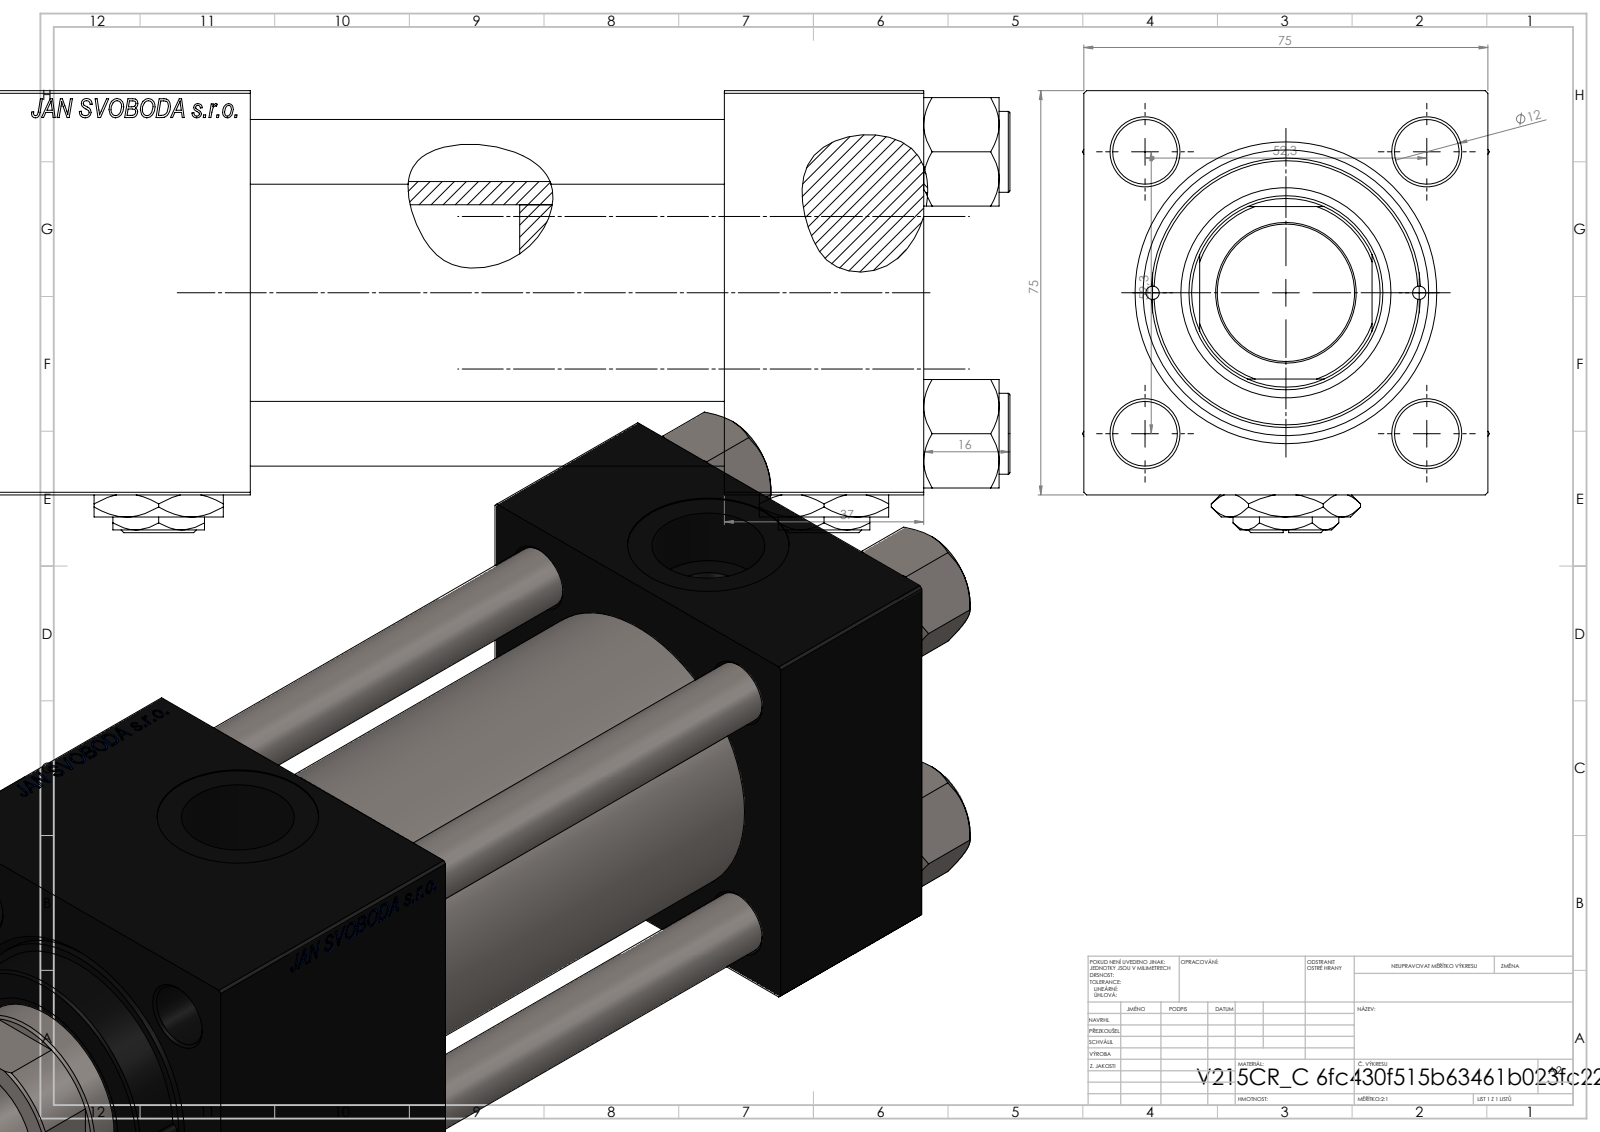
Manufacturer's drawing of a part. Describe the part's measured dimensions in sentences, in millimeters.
The part is named "Zatka_pro_OIL_PORT; V215CR_VCP_C; V215CR_C_Body; NUT_M5_C (+2 more)". Its 3-D file was written by "SolidWorks 2019 (CONFIG_CONTROL_DESIGN)". It is 13 solids with 1255 faces: 575 planar, 102 cylindrical and 578 other. Overall it measures 225 by 82 by 75.54 millimeters. Its volume is 739 321 cubic millimeters and its surface area 178 104 square millimeters. Round holes: 4 of diameter 12, 2 of diameter 2.5, 2 of diameter 7, 2 of diameter 20.96, 2 of diameter 30, 1 of diameter 25.5, 1 of diameter 36, 1 of diameter 39, 1 of diameter 41, 1 of diameter 53. Round bosses or shafts: 4 of diameter 15, 1 of diameter 56, 1 of diameter 50. Partial cylindrical surfaces (rounded edges, fillets, slot ends): 1 of radius 17.5. The main face-to-face distances are 75, 37, 125, 88, 59, 184, 147, 74.8, 155.3, 118.3. The hole center spacings are 26.19, 36.98, 52.3, 57.22, 24.75, 73.96, 49.5, 123.5.
